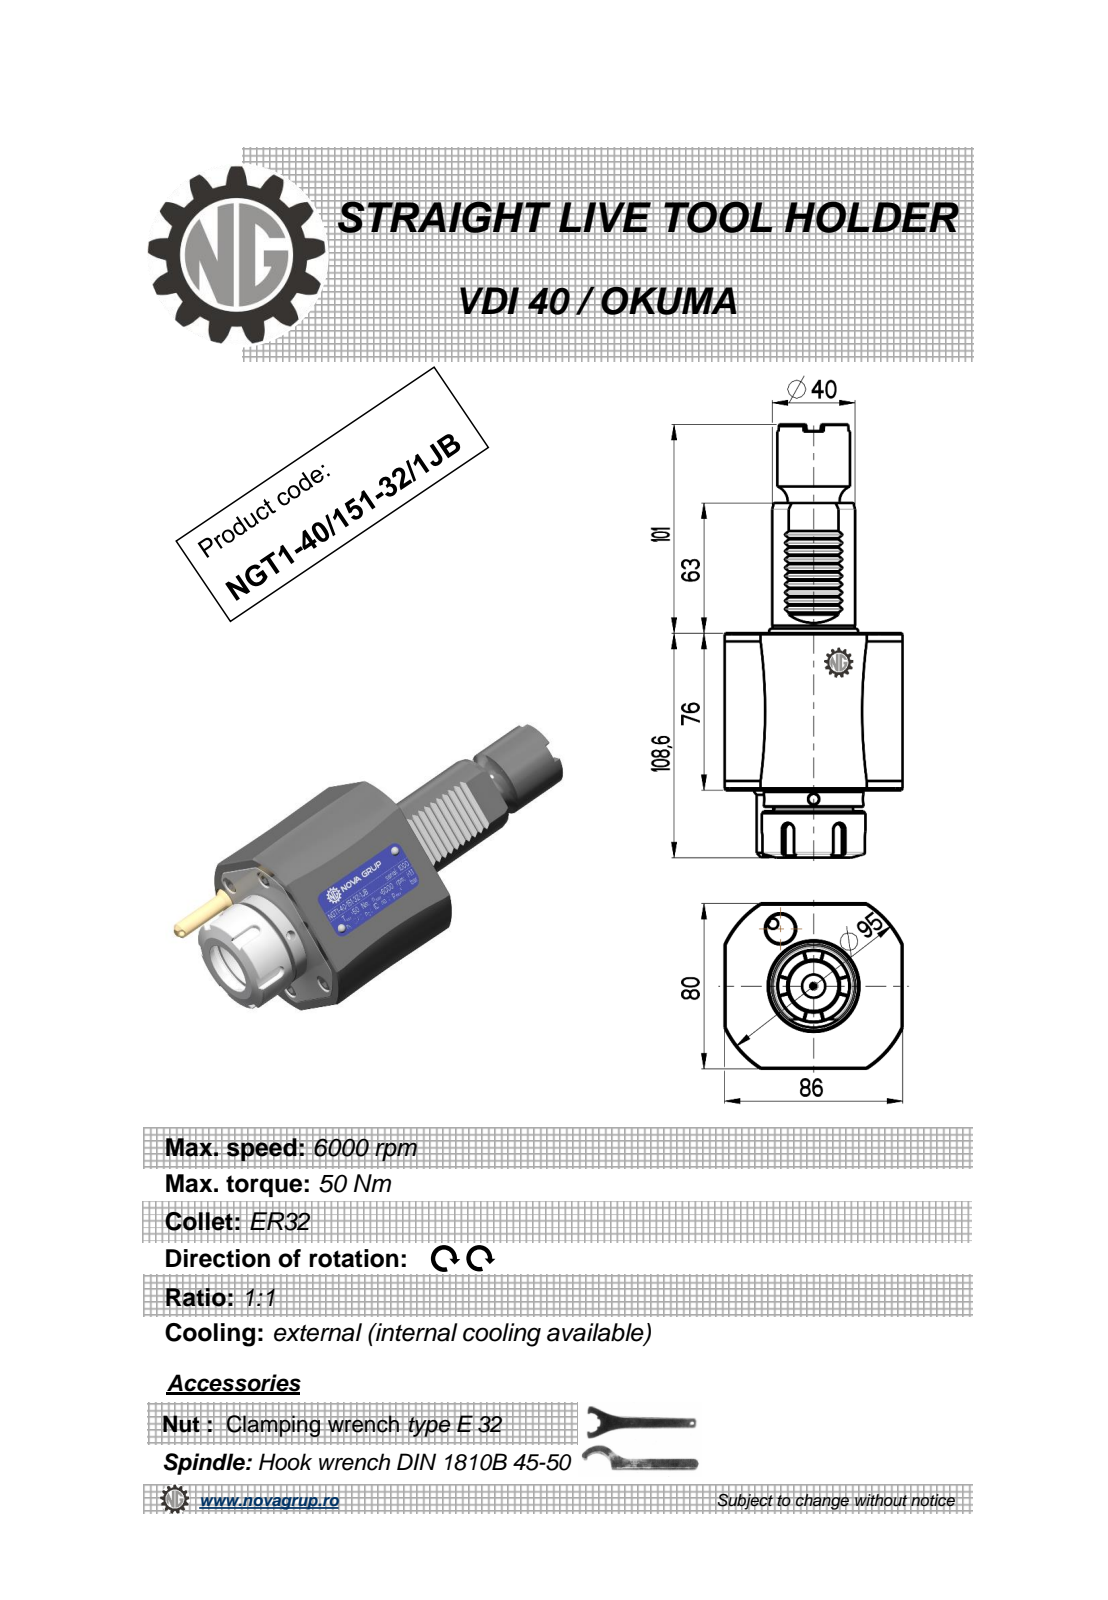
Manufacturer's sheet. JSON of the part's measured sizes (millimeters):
{"part_name": "NGT1_40_151_32_1JB", "step_written_by": "PRO/ENGINEER BY PARAMETRIC TECHNOLOGY CORPORATION, 2010280 (CONFIG_CONTROL_DESIGN)", "units": "millimeters", "bodies": {"solids": 1, "faces": 311, "planar": 116, "cylindrical": 72, "other": 123}, "overall_size": [209.6, 86, 81.6], "volume_mm3": 637790, "surface_area_mm2": 56889, "round_holes": [[5, 3], [3, 1], [27, 1]], "round_bosses_or_shafts": [[50, 1], [48, 1], [41.5, 1], [41, 1], [40, 1], [35, 1], [25, 1], [8, 1]], "partial_cylinders_radius": [[0.3, 10], [0.22, 6], [3, 5], [47.5, 1]], "face_to_face_distances": [76, 80, 86, 2.83, 104.1, 28.1, 5.66, 97.8, 173.8, 201.9], "hole_center_spacings": [40]}
